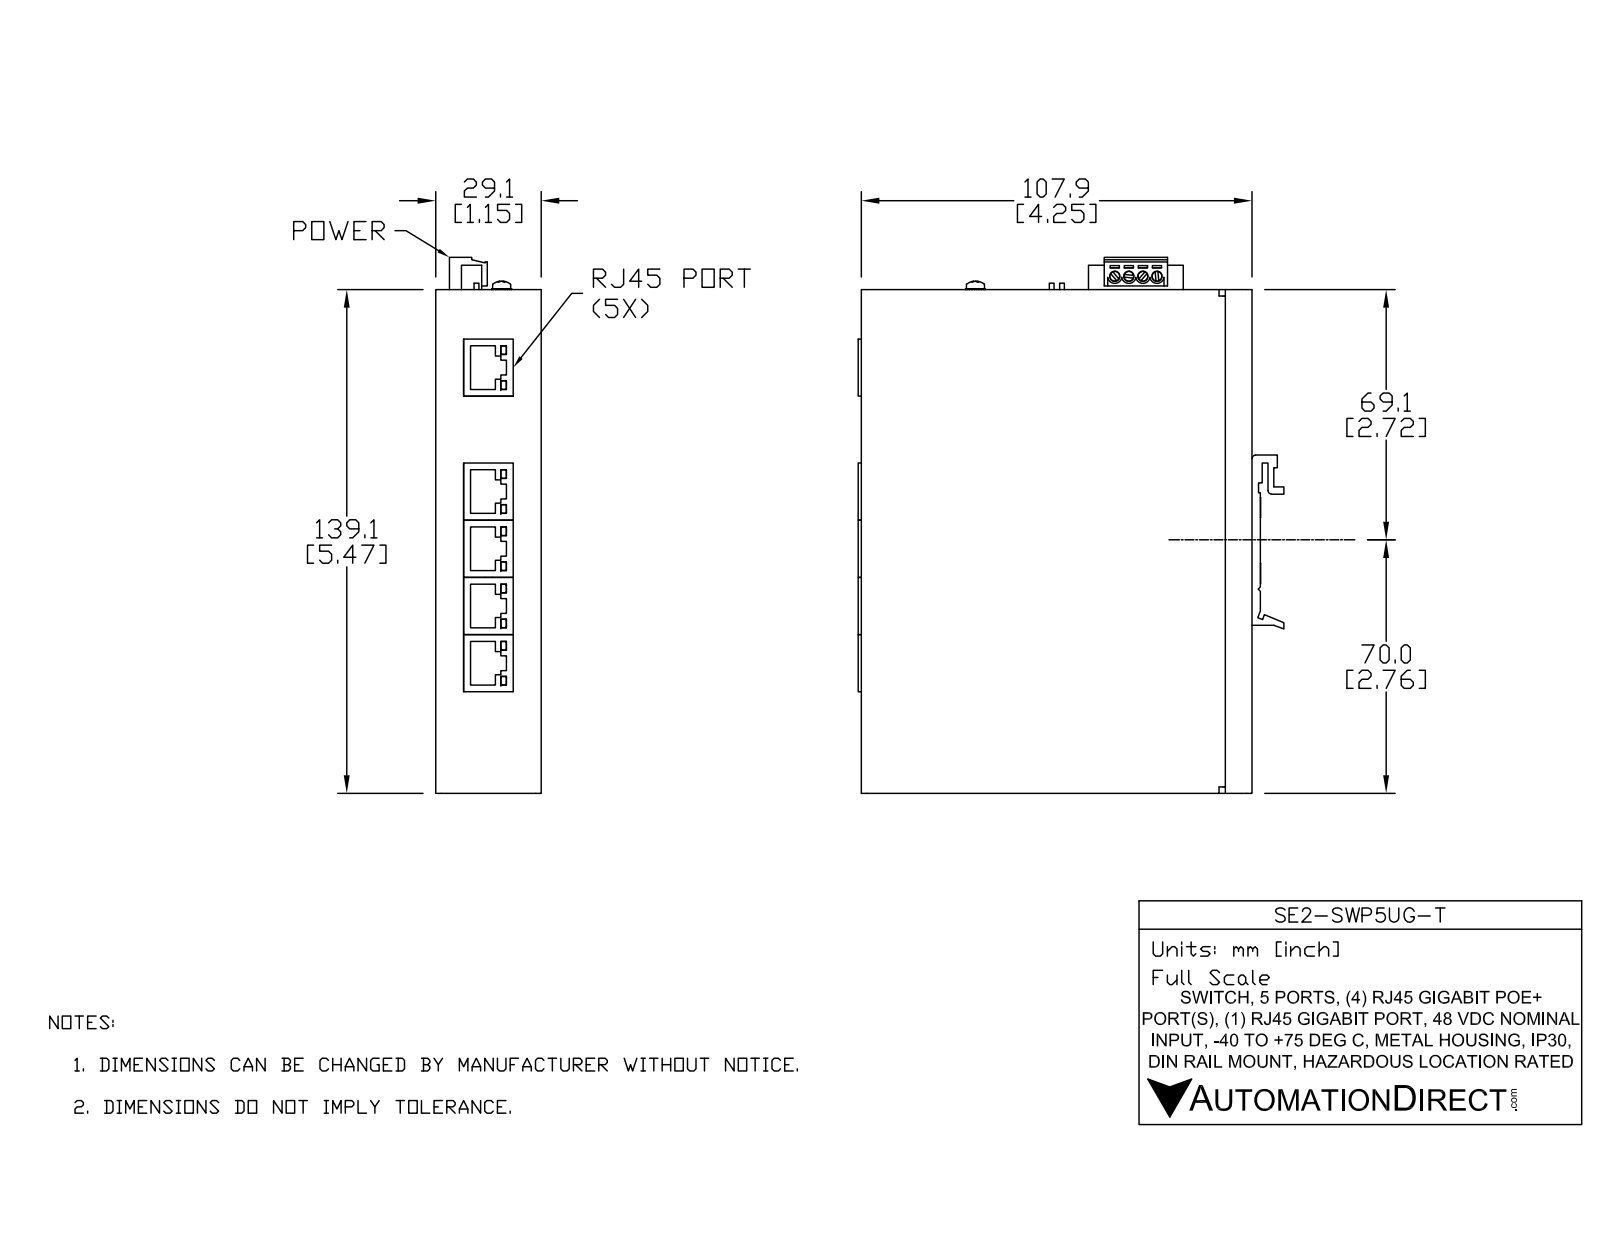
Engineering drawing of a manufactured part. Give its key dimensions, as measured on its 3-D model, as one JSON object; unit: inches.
{"part_name": "SE2-SWP5UG-T", "step_written_by": "SolidWorks 2017 (AUTOMOTIVE_DESIGN)", "units": "inches", "bodies": {"solids": 16, "faces": 780, "planar": 591, "cylindrical": 160, "other": 29}, "overall_size": [5.826, 4.628, 1.148], "volume_in3": 3.639, "surface_area_in2": 179.1, "round_holes": [[0.081, 12], [0.075, 4], [0.11, 4], [0.045, 3], [0.134, 2], [0.155, 2], [0.045, 1], [0.077, 1], [0.11, 1]], "round_bosses_or_shafts": [[0.106, 4], [0.065, 4], [0.217, 2], [0.151, 2], [0.118, 2], [0.197, 1], [0.098, 1]], "partial_cylinders_radius": [[0.007, 18], [0.02, 12], [0.06, 12], [0.3, 8], [0.008, 6], [0.07, 4], [0.077, 4], [0.1, 4]], "face_to_face_distances": [0.04, 0.04, 1.067, 1.107, 1.147, 1.107, 4.208, 5.435, 0.041, 1.107], "hole_center_spacings": [0.153, 0.306, 0.153, 0.441, 0.459, 1.786, 1.822, 2.497]}
